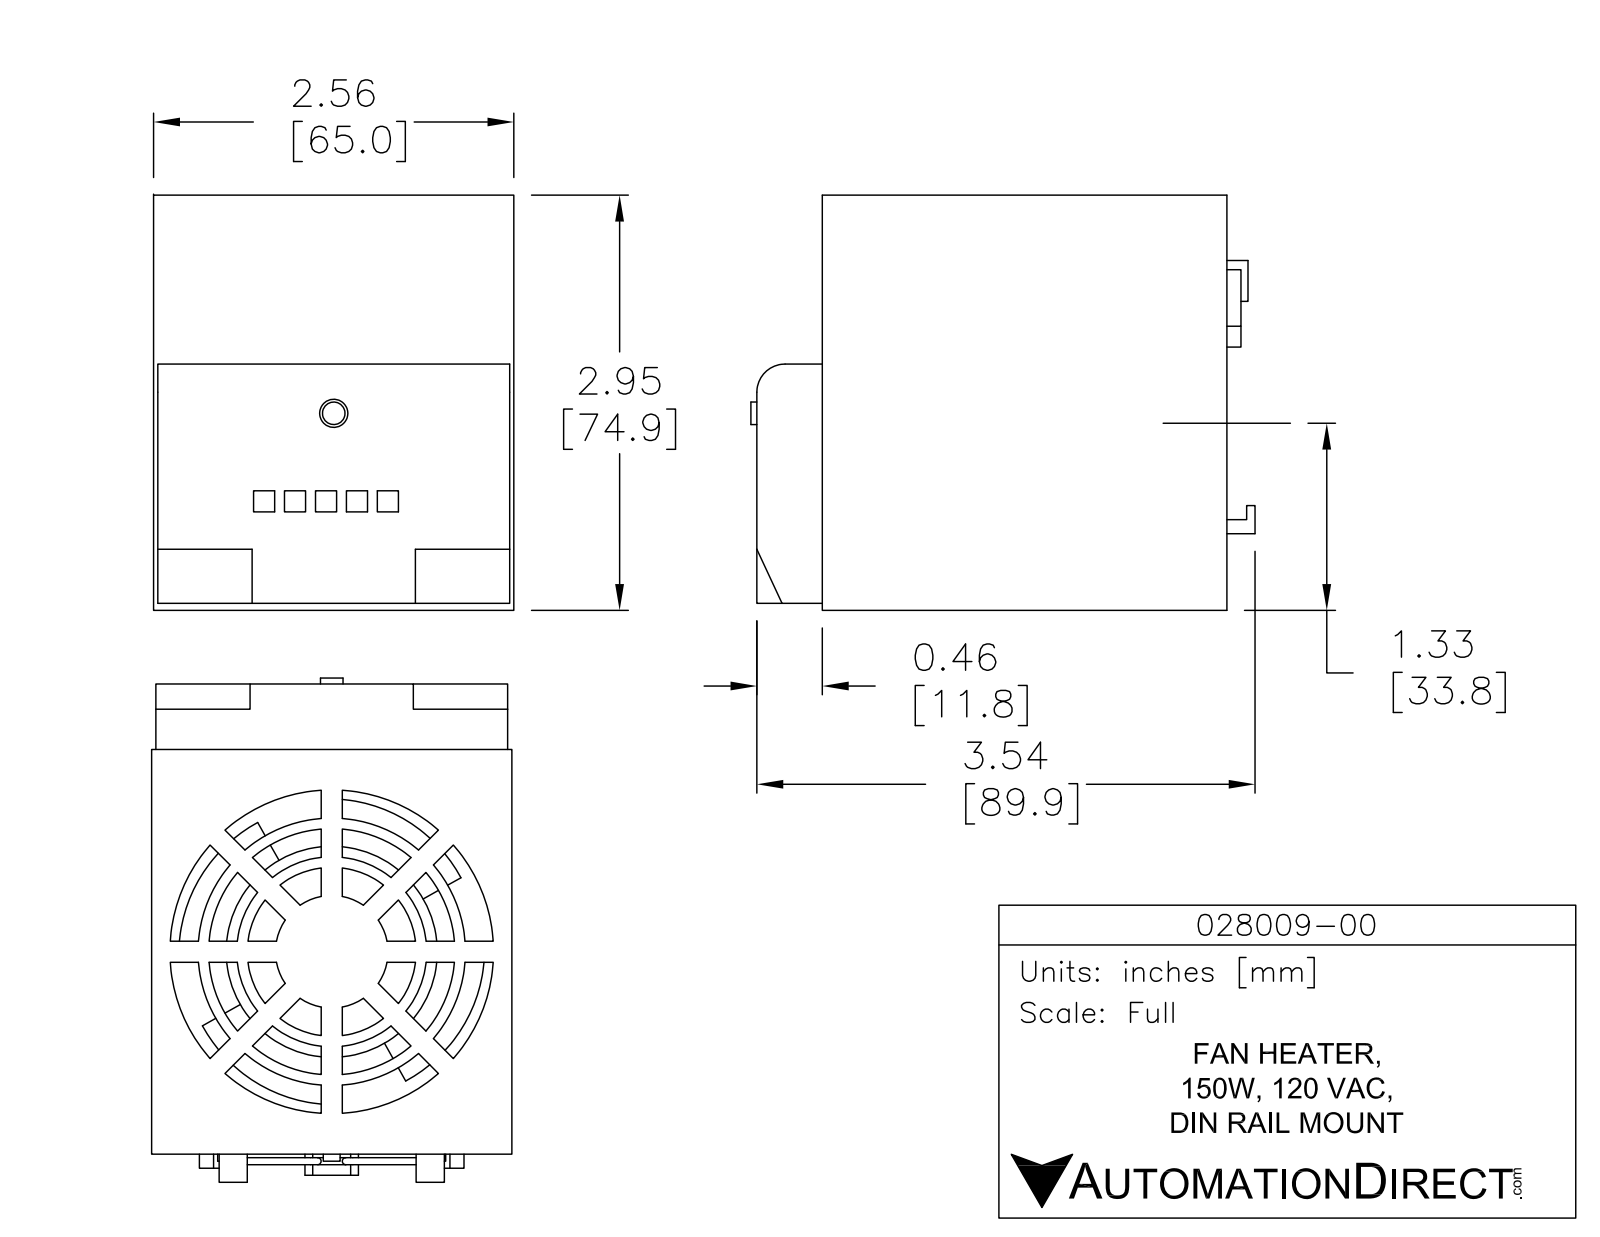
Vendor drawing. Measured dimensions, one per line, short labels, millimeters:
name: 028009-00
written by: SolidWorks 2013 (AUTOMOTIVE_DESIGN)
unit: mm
bodies: 1 solid, 346 faces (174 planar, 133 cylindrical, 39 other)
size: 92.6 × 75.4 × 64.6
volume: 384 800 mm³; area: 38 380 mm²
holes: 1× ⌀7, 1× ⌀57.7
bosses: 1× ⌀5.6
rounds: 44× R1.7, 30× R0.5, 4× R2, 4× R2.5, 1× R4.3, 1× R5.9, 1× R6.4
face distances: 64.6, 72.8, 2.5, 87.1, 0.9, 63.8, 75.3, 70.2, 4.1, 83.1
